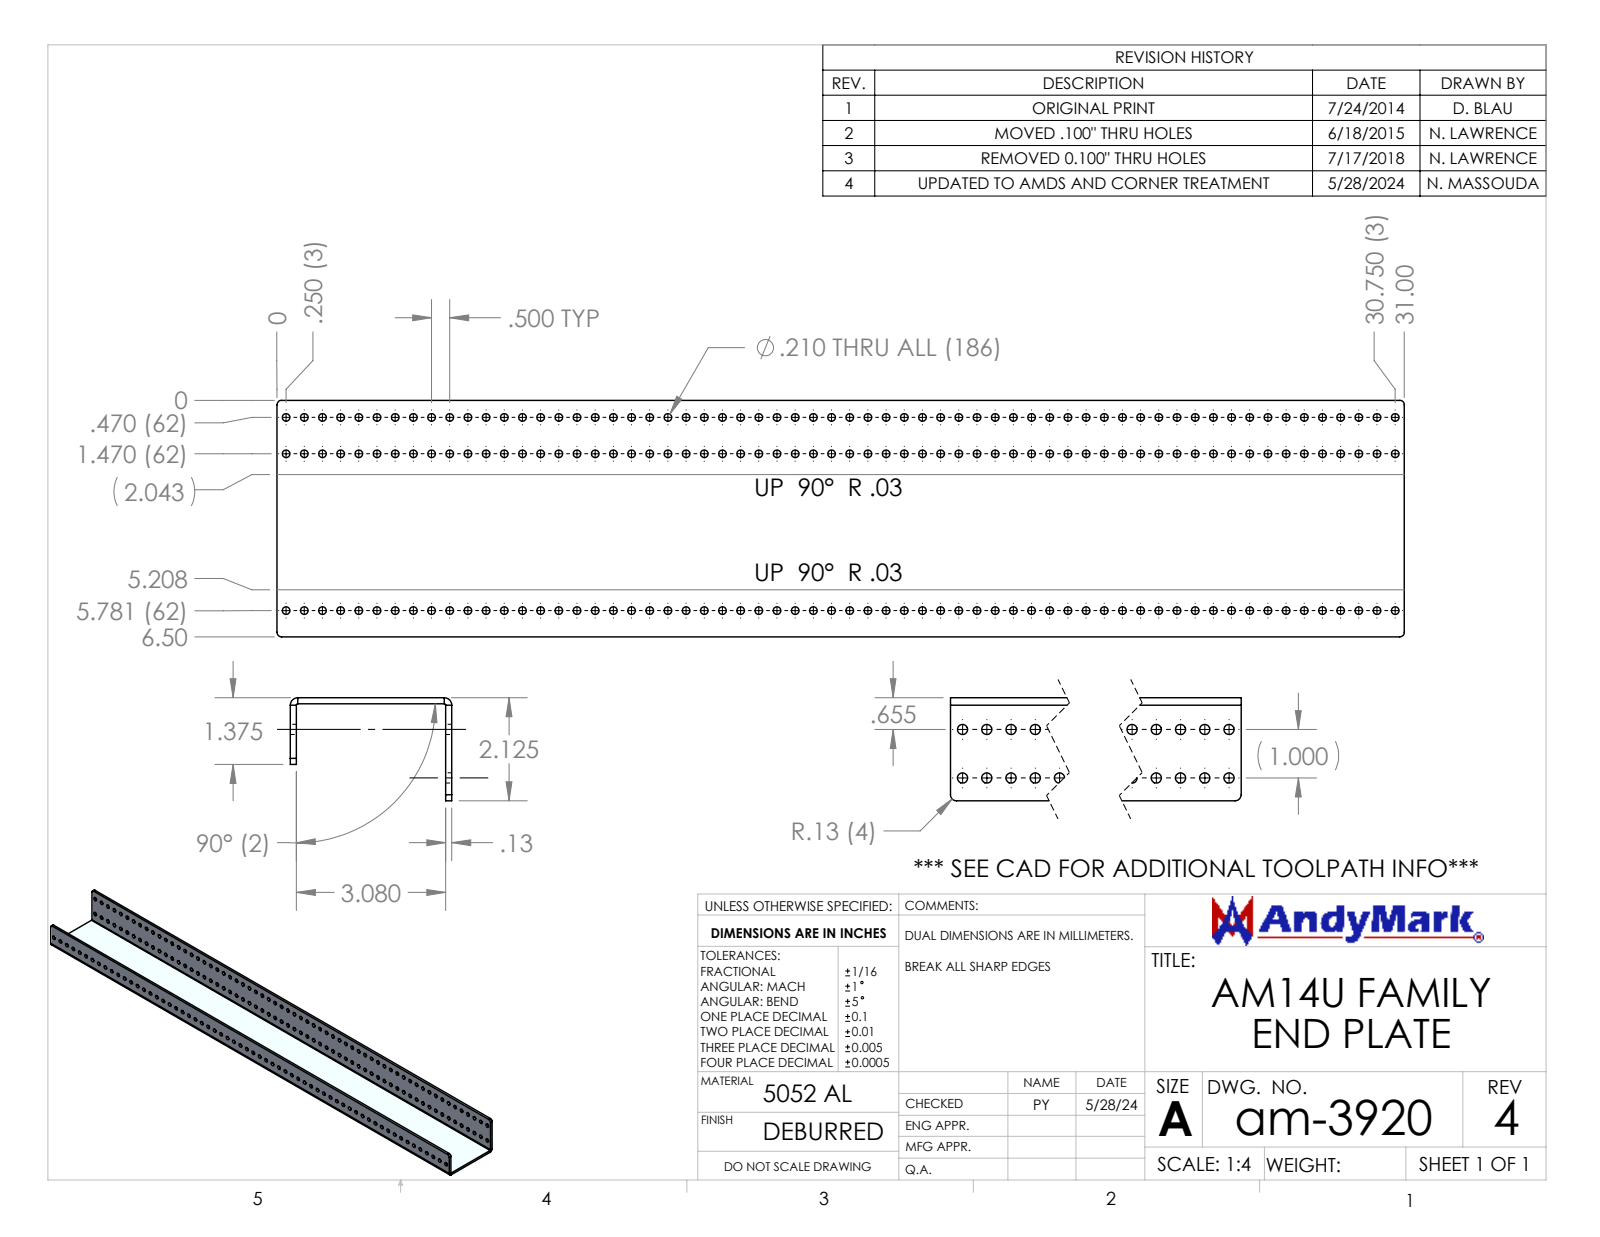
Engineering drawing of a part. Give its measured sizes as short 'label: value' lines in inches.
name: am-3920 AM14U Family End Plate
written by: SolidWorks 2024 (CONFIG_CONTROL_DESIGN)
unit: in
bodies: 1 solid, 398 faces (18 planar, 380 cylindrical, 0 other)
size: 31 × 3.33 × 2.125
volume: 24.38 in³; area: 414.8 in²
holes: 124× ⌀0.21
rounds: 4× R0.125, 2× R0.03, 2× R0.155
face distances: 0.125, 0.125, 3.205, 3.08, 3.33, 3.205, 1.375, 1.25, 2.125, 2
hole spacings: 0.5, 1, 1.5, 2, 2.5, 3, 3.5, 4
